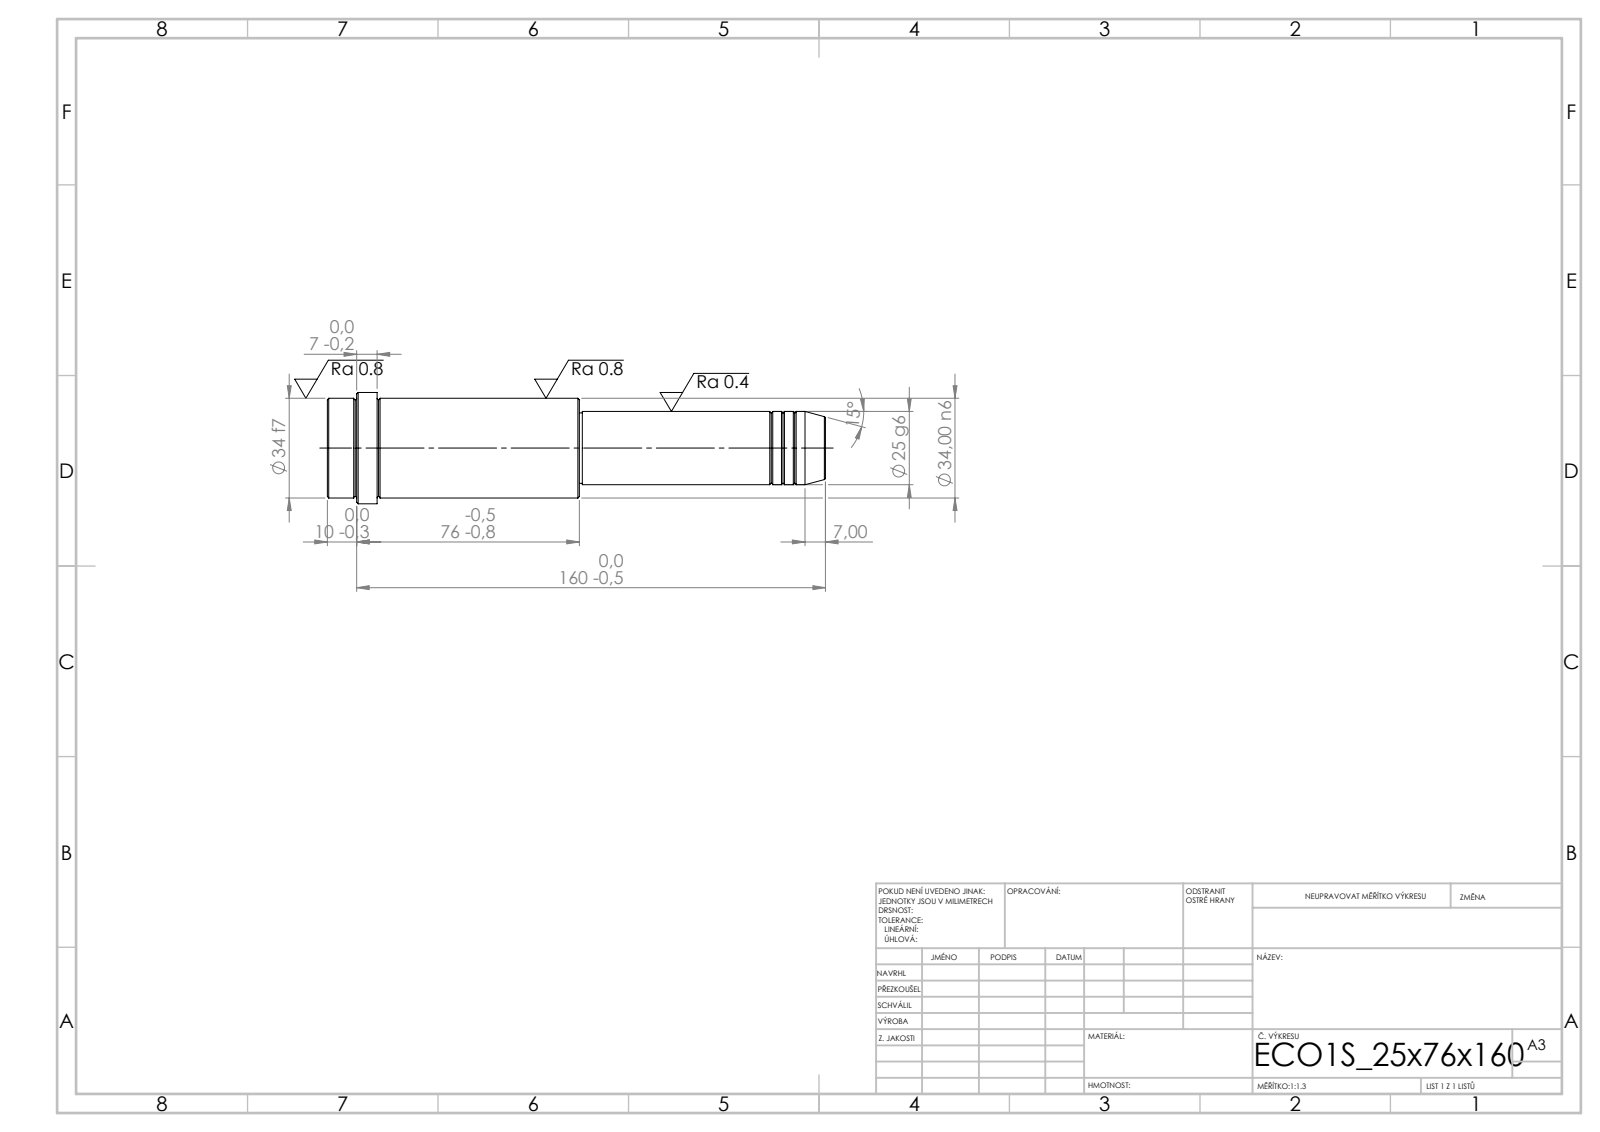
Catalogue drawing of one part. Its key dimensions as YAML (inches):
step_written_by: "SolidWorks 2019 (CONFIG_CONTROL_DESIGN)"
units: inches
bodies: {solids: 1, faces: 52, planar: 6, cylindrical: 16, other: 30}
overall_size: [6.693, 1.496, 1.496]
volume: 7.332
surface_area: 28.19
round_bosses_or_shafts:
  - {diameter: 1.496, count: 1}
  - {diameter: 1.339, count: 1}
  - {diameter: 0.984, count: 1}
  - {diameter: 0.945, count: 1}
face_to_face_distances: [3.386, 3.307, 6.693, 6.024, 2.717, 0.669, 6.299, 2.992, 0.276, 0.394]
